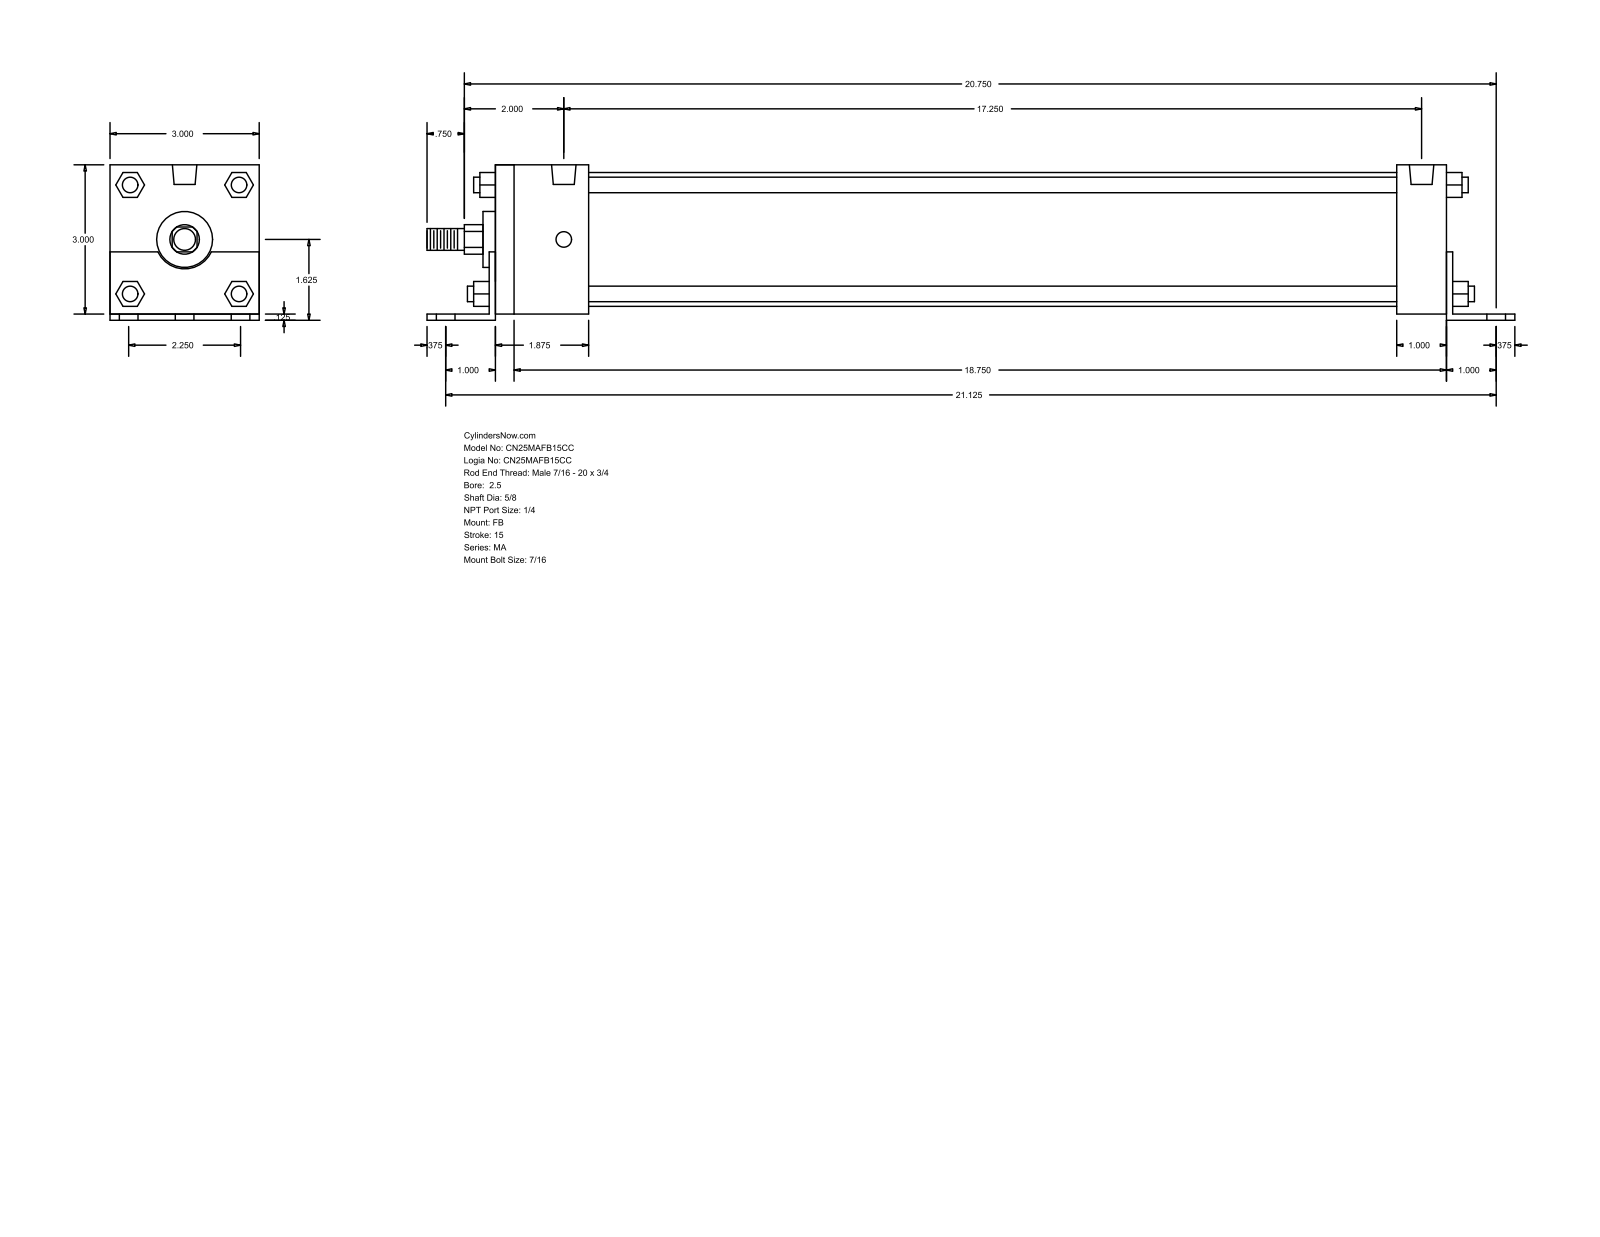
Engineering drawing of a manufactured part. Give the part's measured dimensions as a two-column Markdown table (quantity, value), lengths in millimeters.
| quantity | value |
| --- | --- |
| part name | MA_FB__0250_0.625 |
| STEP written by | GSSL Pune (CONFIG_CONTROL_DESIGN) |
| units | millimeters |
| bodies | 0 solids, 140 faces (105 planar, 35 cylindrical, 0 other) |
| overall size | 555.62 × 79.38 × 76.2 |
| round holes (diameter × count) | 11.11 × 6, 7.94 × 4, 12.49 × 2 |
| round bosses / shafts (diameter × count) | 7.94 × 4, 68.33 × 1, 28.57 × 1, 15.88 × 1, 11.11 × 1 |
| partial cylindrical surfaces (radius × count) | 7.54 × 1, 15.05 × 1 |
| main face-to-face distances | 76.2, 3.17, 79.37, 485.77, 492.12, 3.18, 488.94, 47.62, 25.4, 488.95 |
| hole center spacings | 28.57, 537.34, 536.58, 47.62, 57.14, 66.75, 438.15, 477.11 |
